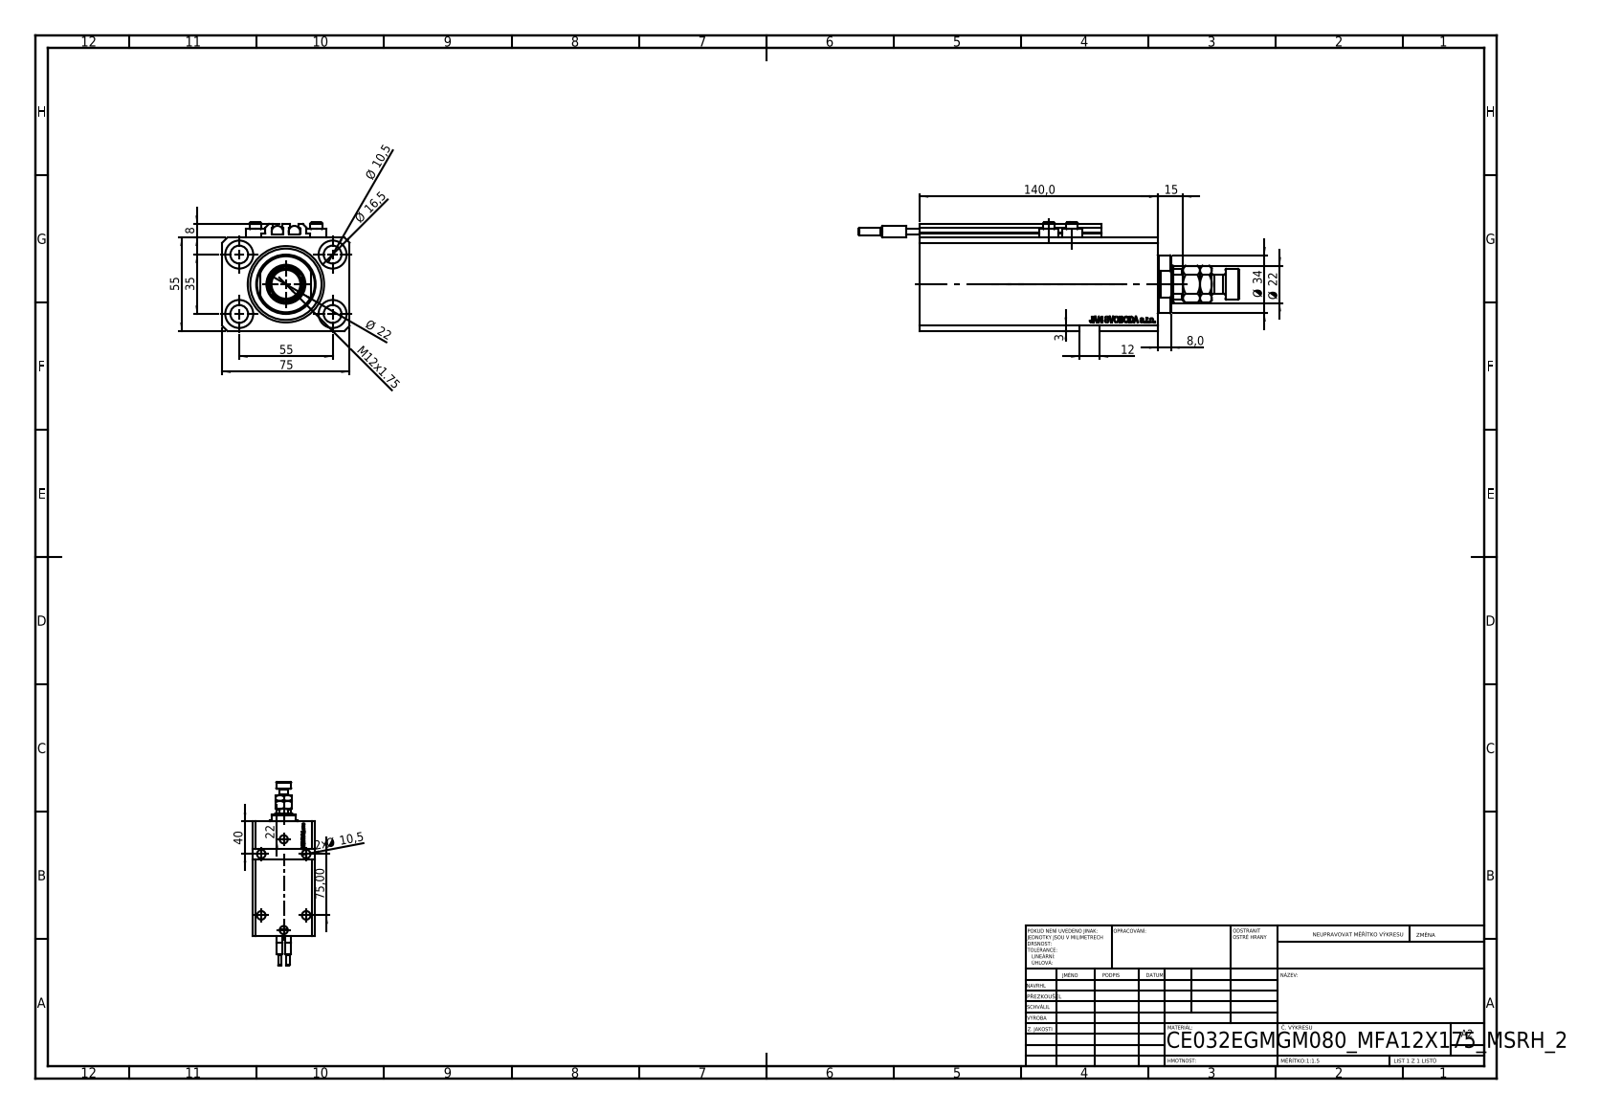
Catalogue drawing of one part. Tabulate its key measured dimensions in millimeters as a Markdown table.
| quantity | value |
| --- | --- |
| part name | ALLEN BOLT V250CE; V250CE_E_Body; V250CE_C_VCP; MFA (+2 more) |
| STEP written by | SolidWorks 2019 (CONFIG_CONTROL_DESIGN) |
| units | millimeters |
| bodies | 11 solids, 1188 faces (562 planar, 162 cylindrical, 464 other) |
| overall size | 224 × 75 × 64 |
| volume | 496 860 mm³ |
| surface area | 120 750 mm² |
| round holes (diameter × count) | 10.5 × 9, 1.25 × 4, 4 × 4, 16.5 × 4, 10 × 2, 13.16 × 2, 20 × 2, 22 × 1, 32 × 1, 45 × 1 |
| round bosses / shafts (diameter × count) | 11.6 × 4, 7 × 4, 6.8 × 2, 6.5 × 2, 4 × 2, 34 × 1, 18 × 1, 11 × 1 |
| partial cylindrical surfaces (radius × count) | 0.2 × 10, 10.5 × 1 |
| main face-to-face distances | 55, 75, 15, 3, 57, 140, 125, 2.5, 9.9, 2 |
| hole center spacings | 32.6, 32.87, 55, 96.98, 13.6, 14.09, 25.81, 32.58 |
